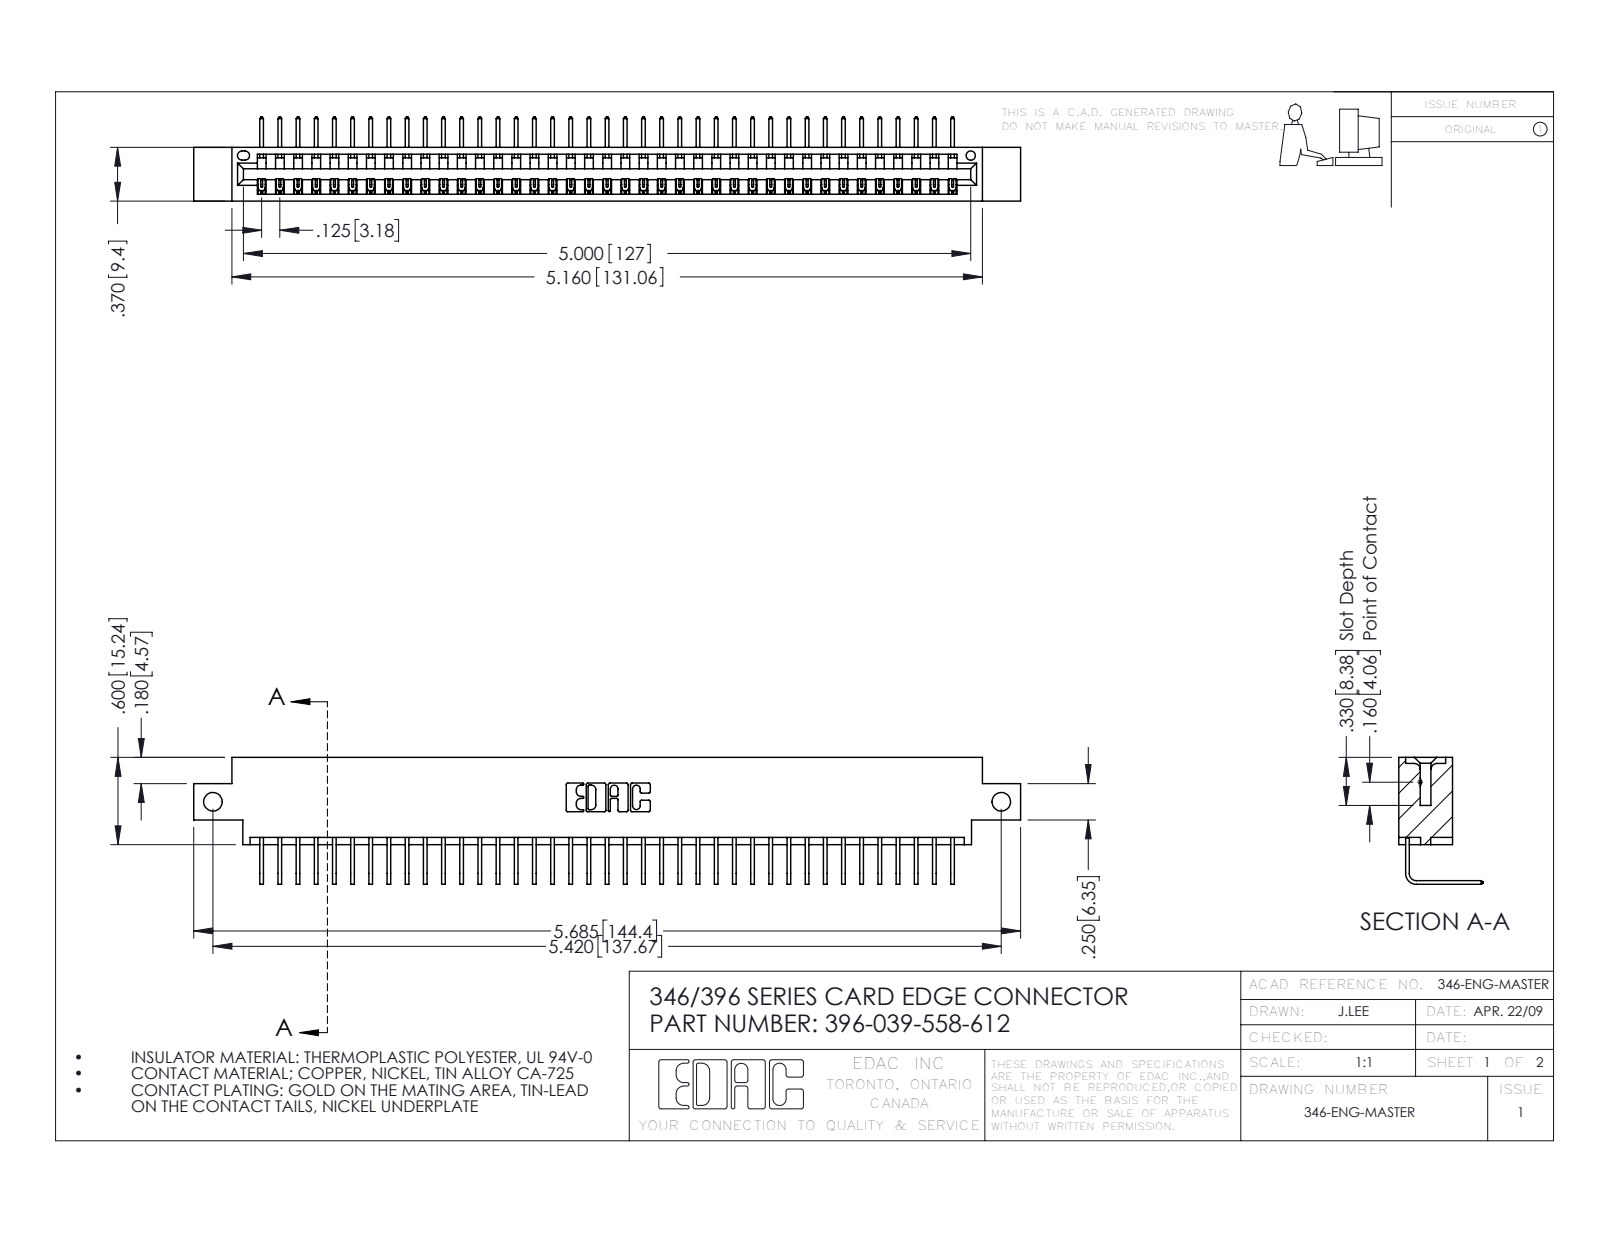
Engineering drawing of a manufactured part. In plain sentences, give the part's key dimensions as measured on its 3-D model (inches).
The part is named "345-292-001_558 Tail - 2; 396-039-558-612; 346 Part_0.170 Offset - Side Mount". Its 3-D file was written by "SolidWorks 2016 (CONFIG_CONTROL_DESIGN)". It is 40 solids with 2466 faces: 1718 planar, 748 cylindrical and 0 other. Overall it measures 5.685 by 0.873 by 0.58 inches. Its volume is 0.835 cubic inches and its surface area 27.69 square inches. Round holes: 2 of diameter 0.128, 1 of diameter 0.064. Partial cylindrical surfaces (rounded edges, fillets, slot ends): 78 of radius 0.006, 22 of radius 0.01, 6 of radius 0.007, 6 of radius 0.031, 3 of radius 0.026, 2 of radius 0.031, 2 of radius 0.04, 1 of radius 0.014. The main face-to-face distances are 0.322, 0.048, 0.37, 0.25, 0.298, 0.025, 0.072, 0.148, 0.222, 0.1. The hole center spacings are 5.42.
